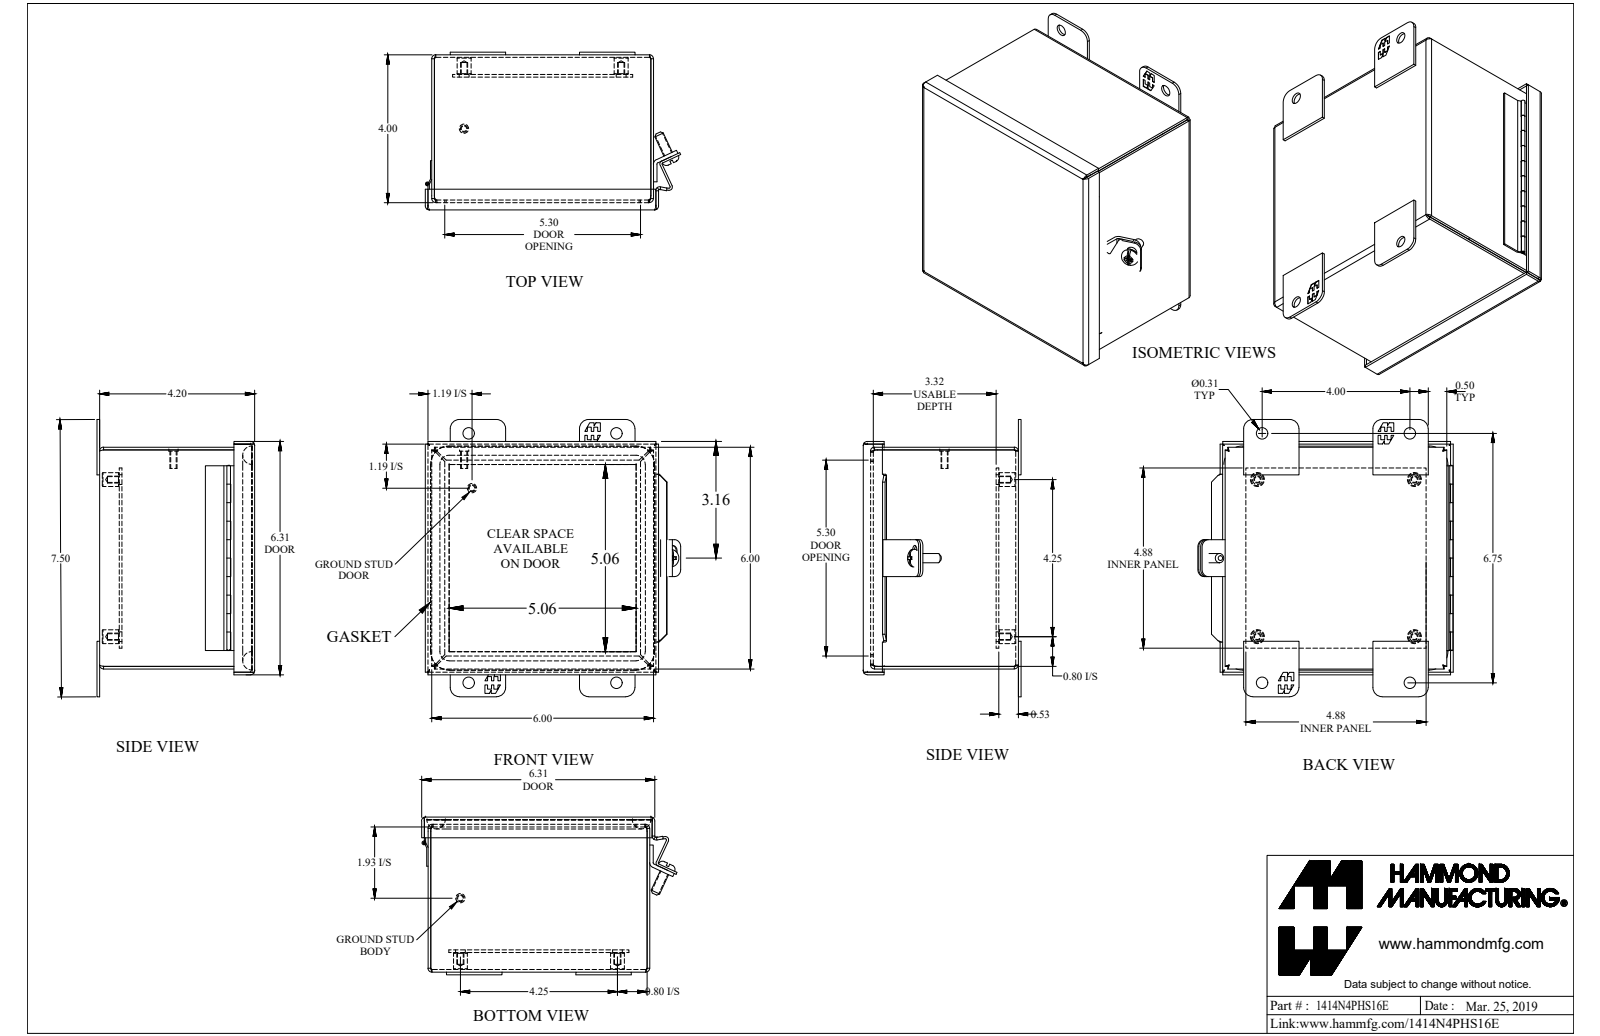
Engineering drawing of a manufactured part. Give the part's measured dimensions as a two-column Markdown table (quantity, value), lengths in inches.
| quantity | value |
| --- | --- |
| part name | 1414N4PHS16E |
| STEP written by | SolidWorks 2018 (AUTOMOTIVE_DESIGN) |
| units | inches |
| bodies | 19 solids, 539 faces (355 planar, 133 cylindrical, 51 other) |
| overall size | 7.5 × 6.903 × 4.269 |
| volume | 18.93 in³ |
| surface area | 521.4 in² |
| round holes (diameter × count) | 0.156 × 4, 0.265 × 4, 0.313 × 4, 0.05 × 1, 0.213 × 1 |
| round bosses / shafts (diameter × count) | 0.375 × 4, 0.25 × 3, 0.19 × 2, 0.48 × 1, 0.1 × 1, 0.045 × 1 |
| partial cylindrical surfaces (radius × count) | 0.25 × 24, 0.036 × 8, 0.108 × 8, 0.079 × 4, 0.118 × 4, 0.188 × 4, 0.499 × 4, 0.01 × 2 |
| main face-to-face distances | 0.072, 5.928, 0.081, 0.532, 5.856, 6, 4.116, 4.197, 4.125, 4.044 |
| hole center spacings | 4.25, 4.25, 4.31, 1.256, 5.502, 6.01, 6.875, 1.257 |
